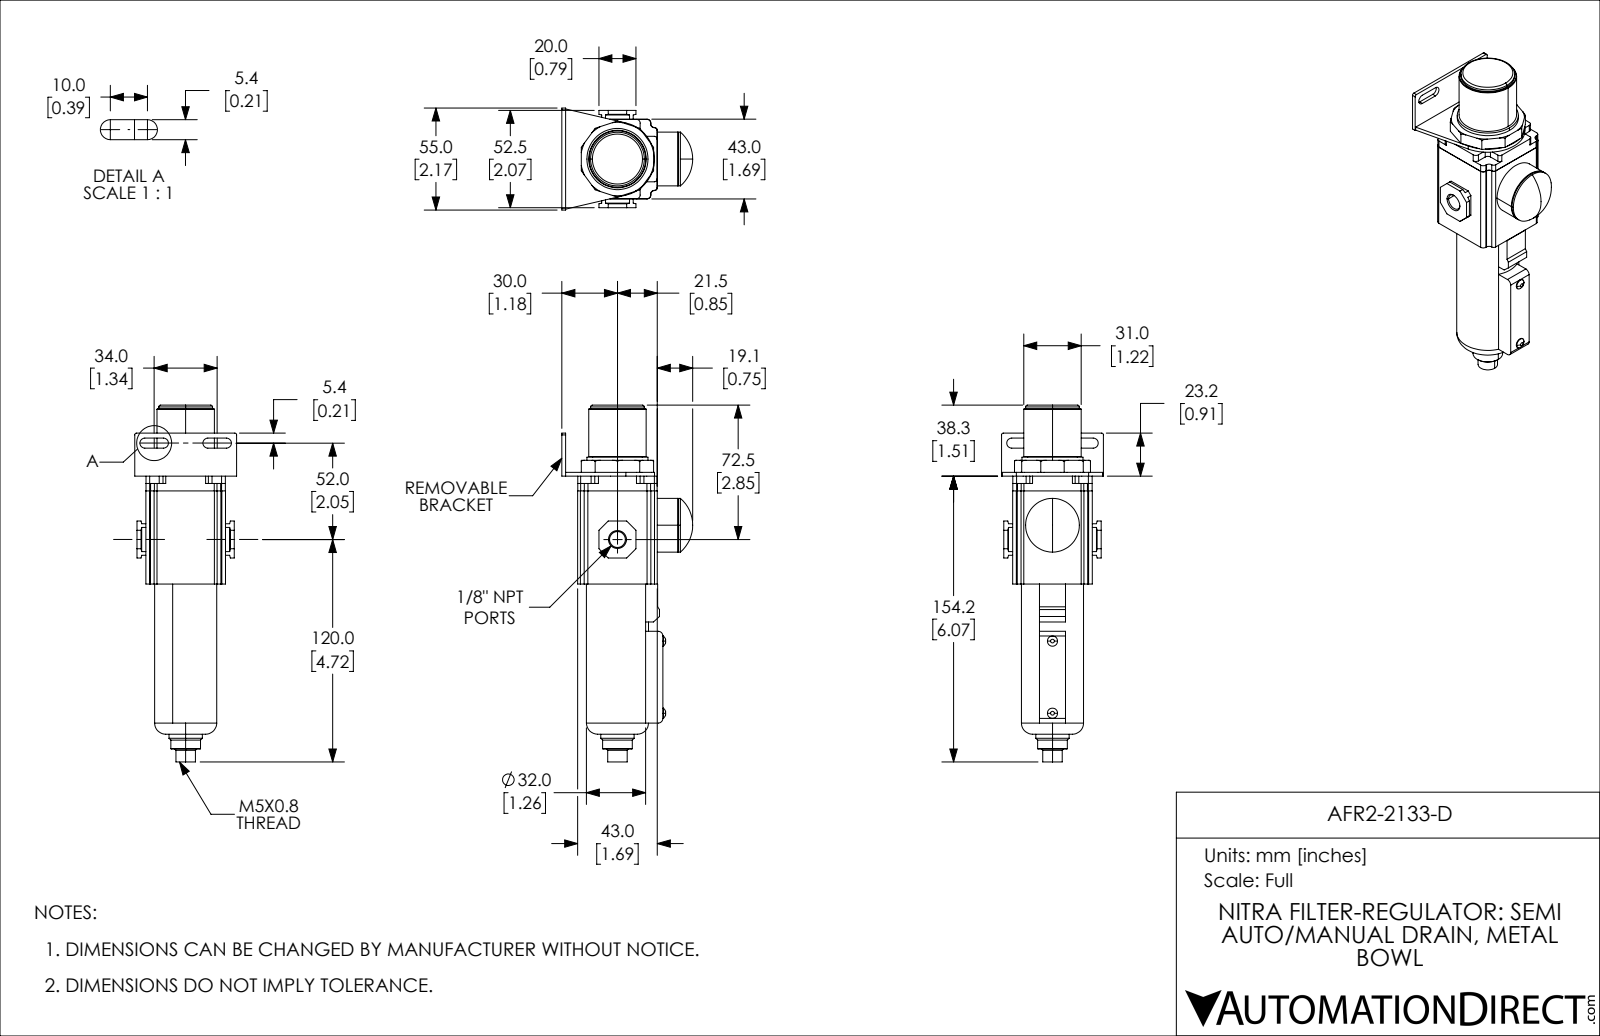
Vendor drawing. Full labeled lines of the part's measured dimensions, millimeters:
Part name (STEP PRODUCT): AFR2-2133-D
STEP written by: SolidWorks 2019 (CONFIG_CONTROL_DESIGN)
Units: millimetres
Bodies: 1 solid, 237 faces (126 planar, 75 cylindrical, 36 other)
Overall size (bounding box): 192.5 × 70.62 × 55
Volume: 231 878 mm³ · Surface area: 34 099 mm²
Round holes (diameter × count): ⌀4.13 ×1, ⌀8.57 ×1
Round bosses / shafts (diameter × count): ⌀29 ×2, ⌀5.5 ×2, ⌀33.5 ×1, ⌀33 ×1, ⌀31 ×1, ⌀26.78 ×1, ⌀18 ×1, ⌀16 ×1
Partial cylindrical surfaces — rounded edges, fillets, slot ends (radius × count): R2 ×24, R1.5 ×12, R2.7 ×4, R1 ×2, R2.5 ×2, R20 ×1
Main face-to-face distances: 43, 2, 8.5, 6.5, 14.5, 28.5, 49.5, 52.5, 51.5, 42.9
